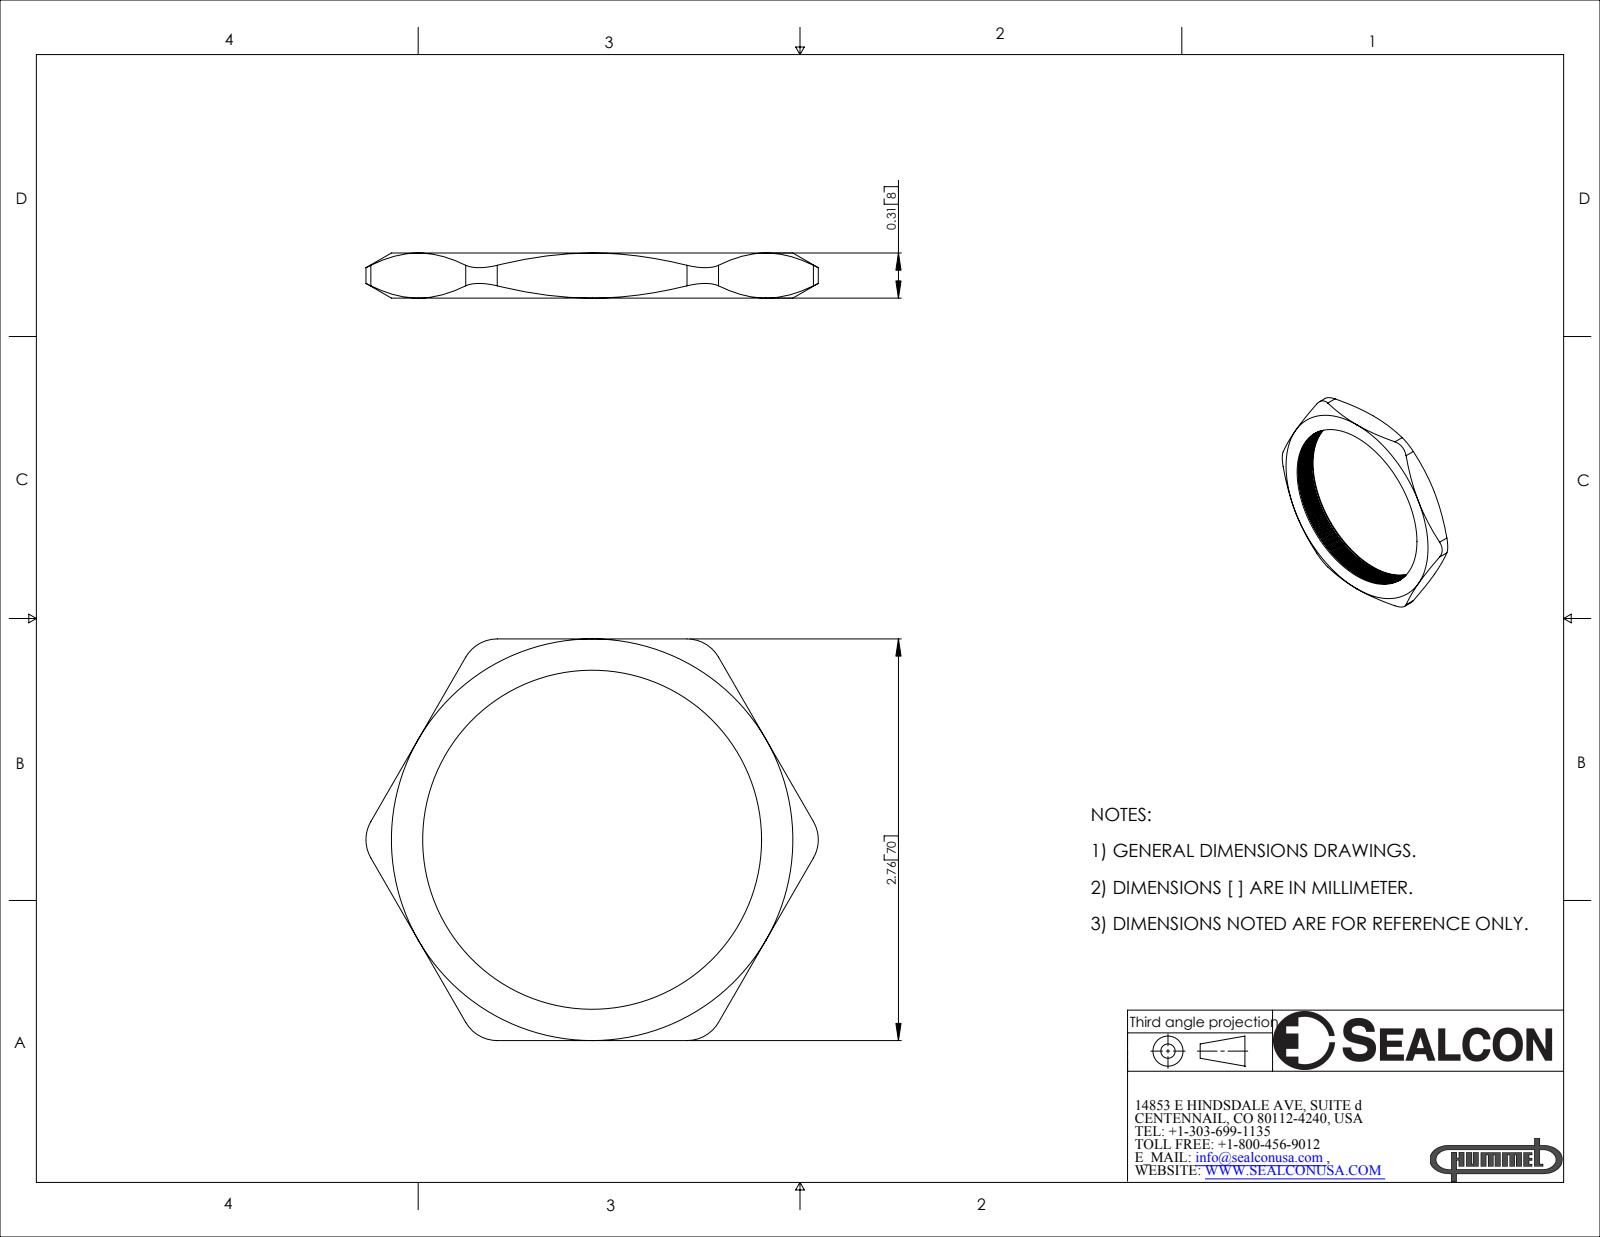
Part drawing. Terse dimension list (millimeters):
name: NP-48
written by: SolidWorks 2007 (CONFIG_CONTROL_DESIGN)
unit: mm
bodies: 1 solid, 101 faces (8 planar, 31 cylindrical, 62 other)
size: 79 × 70.1 × 7.9
volume: 10 700 mm³; area: 7 297 mm²
holes: 1× ⌀59.2
rounds: 6× R6.4
face distances: 7.9, 70.1
